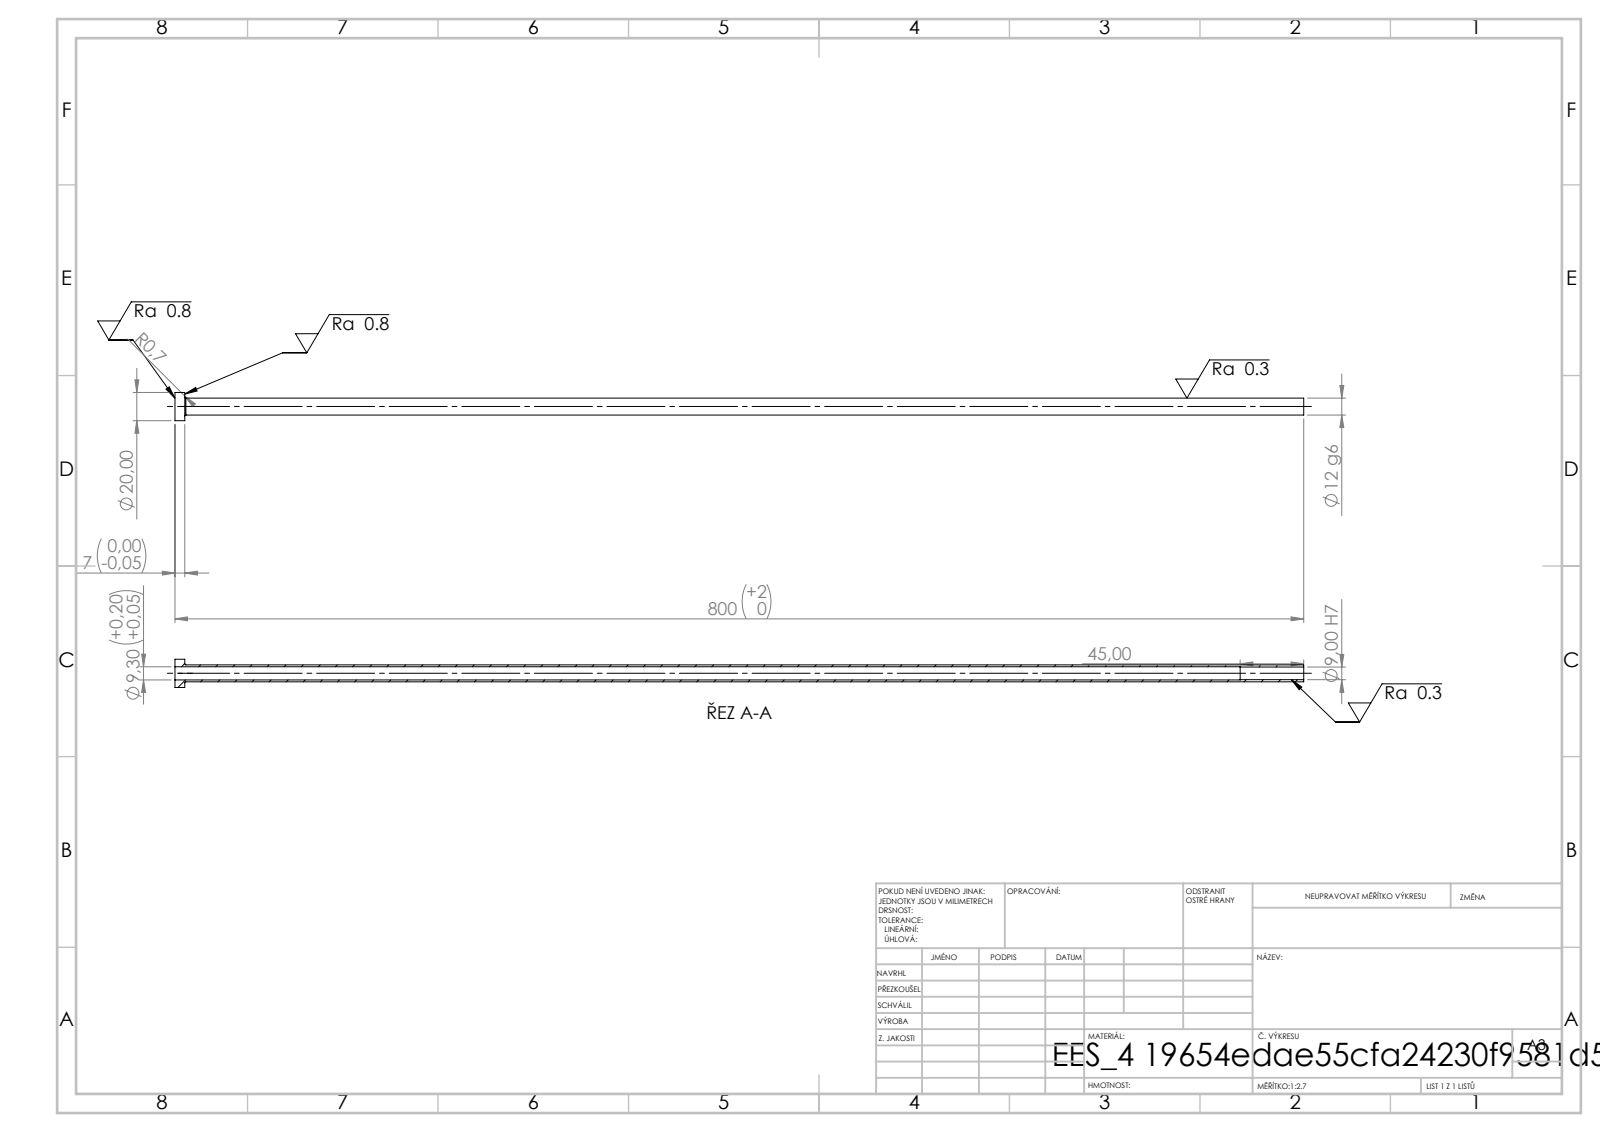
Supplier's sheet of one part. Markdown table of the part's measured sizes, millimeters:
| quantity | value |
| --- | --- |
| STEP written by | SolidWorks 2019 (CONFIG_CONTROL_DESIGN) |
| units | millimeters |
| bodies | 1 solid, 14 faces (4 planar, 8 cylindrical, 2 other) |
| overall size | 800 × 20 × 20 |
| volume | 37 740 mm³ |
| surface area | 54 156 mm² |
| round holes (diameter × count) | 9 × 1, 9.3 × 1 |
| round bosses / shafts (diameter × count) | 20 × 1, 12 × 1 |
| main face-to-face distances | 7, 800, 793, 755, 748, 45 |
